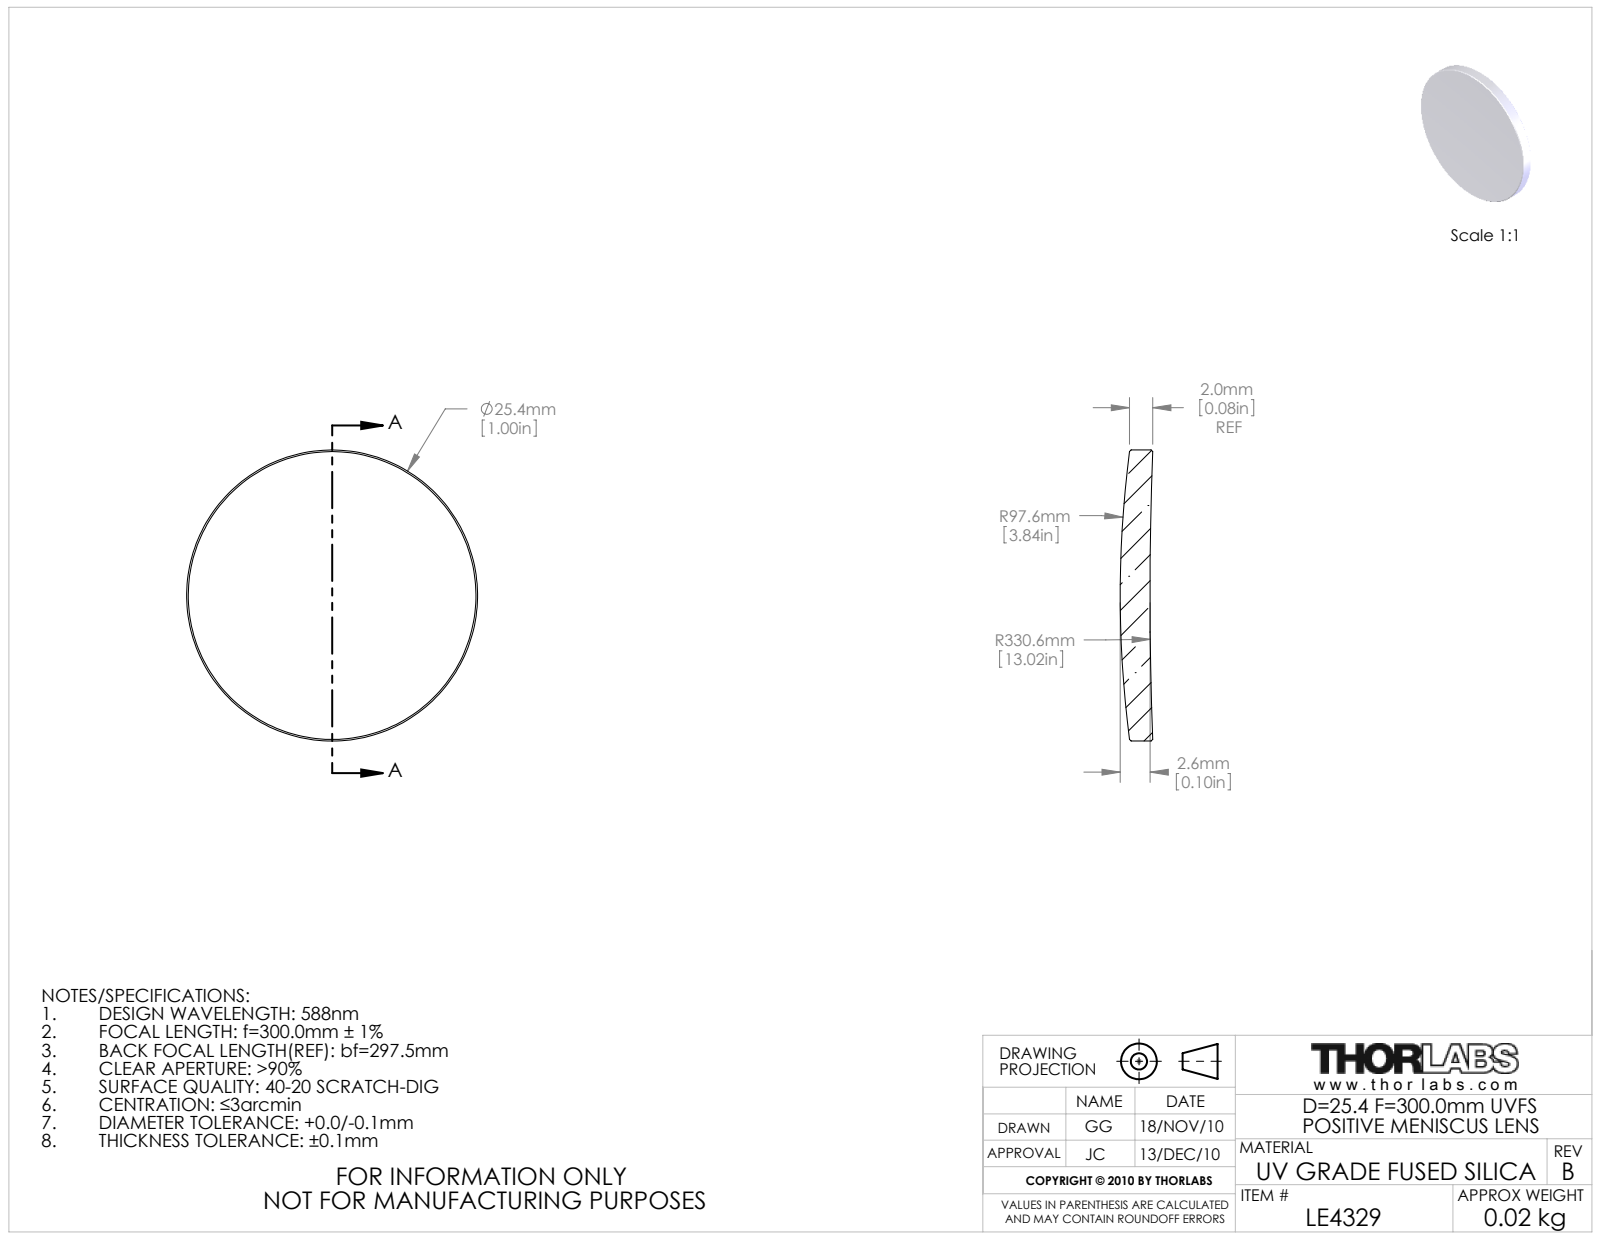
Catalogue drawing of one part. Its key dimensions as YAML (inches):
part_name: "4208-E0W"
step_written_by: "SolidWorks 2009 (AUTOMOTIVE_DESIGN)"
units: inches
bodies: {solids: 1, faces: 10, planar: 0, cylindrical: 2, other: 8}
overall_size: [1, 1, 0.112]
volume: 0.071
surface_area: 1.804
round_bosses_or_shafts:
  - {diameter: 1, count: 1}
